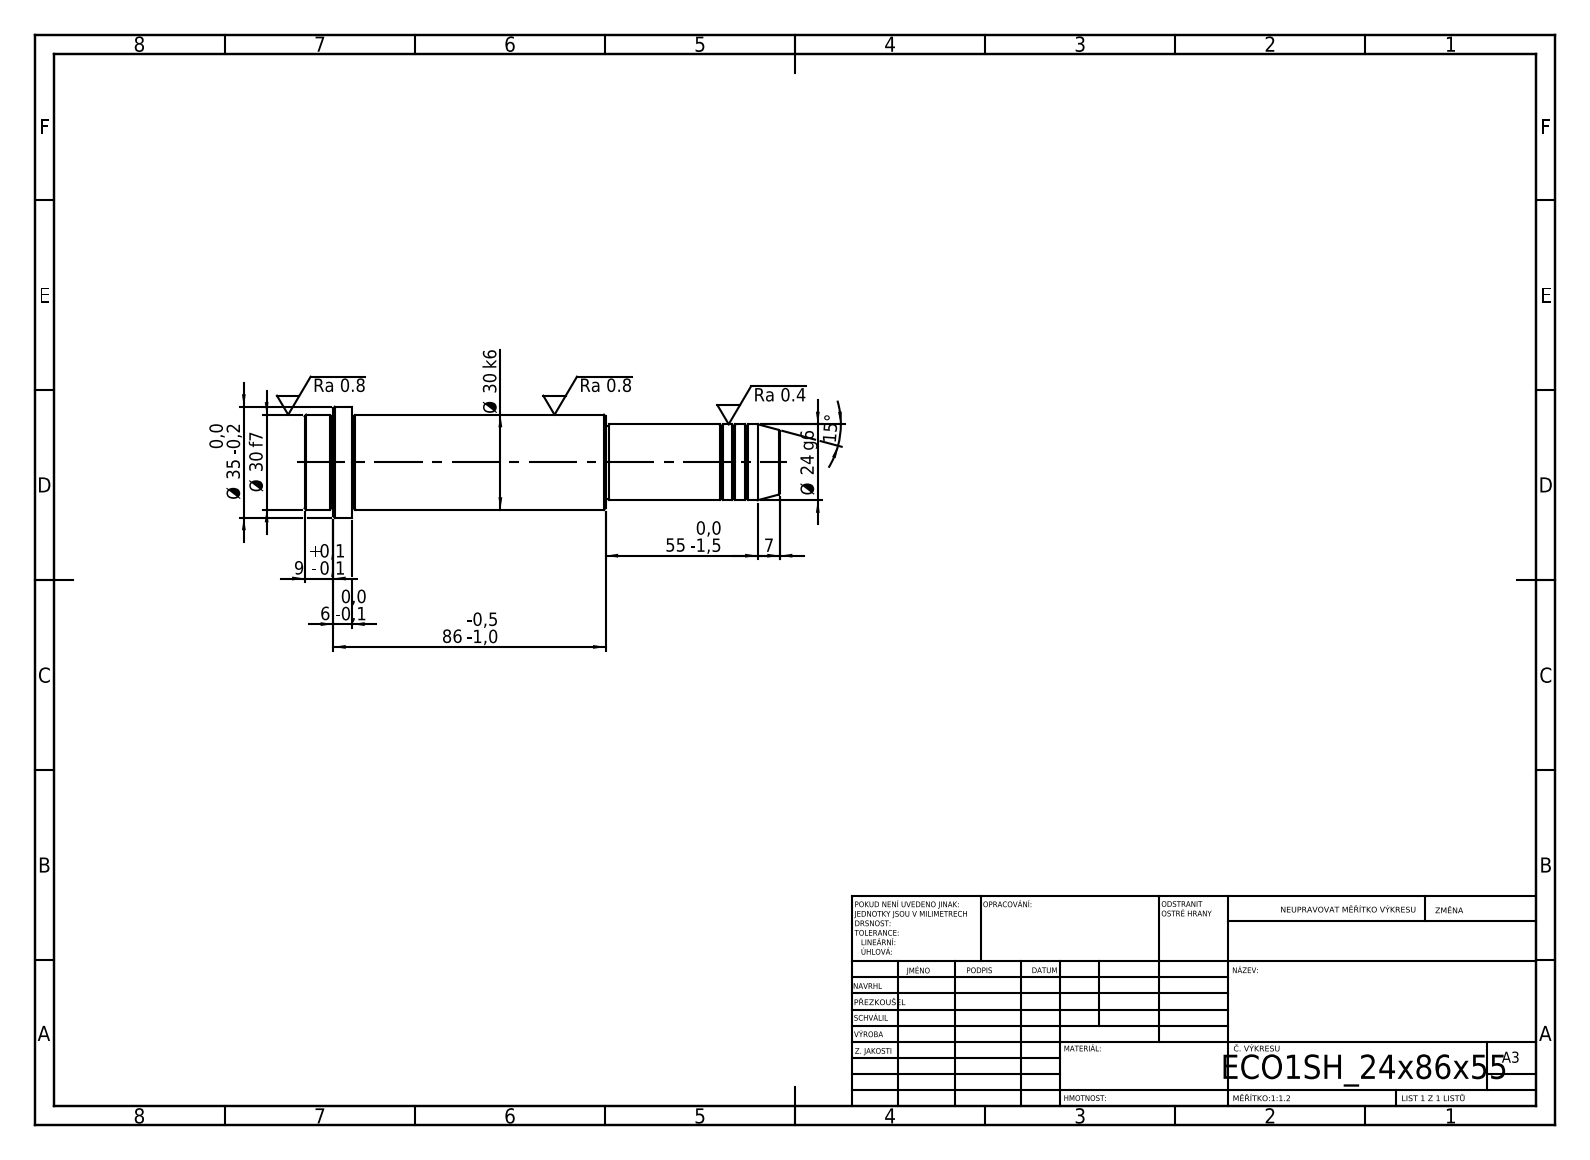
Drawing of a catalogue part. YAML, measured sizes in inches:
step_written_by: "SolidWorks 2019 (CONFIG_CONTROL_DESIGN)"
units: inches
bodies: {solids: 1, faces: 52, planar: 6, cylindrical: 16, other: 30}
overall_size: [5.906, 1.378, 1.378]
volume: 5.667
surface_area: 23.5
round_bosses_or_shafts:
  - {diameter: 1.378, count: 1}
  - {diameter: 1.181, count: 1}
  - {diameter: 0.945, count: 1}
  - {diameter: 0.906, count: 1}
face_to_face_distances: [5.906, 5.315, 0.591, 2.165, 3.15, 3.74, 5.551, 3.386, 0.236, 0.354]
